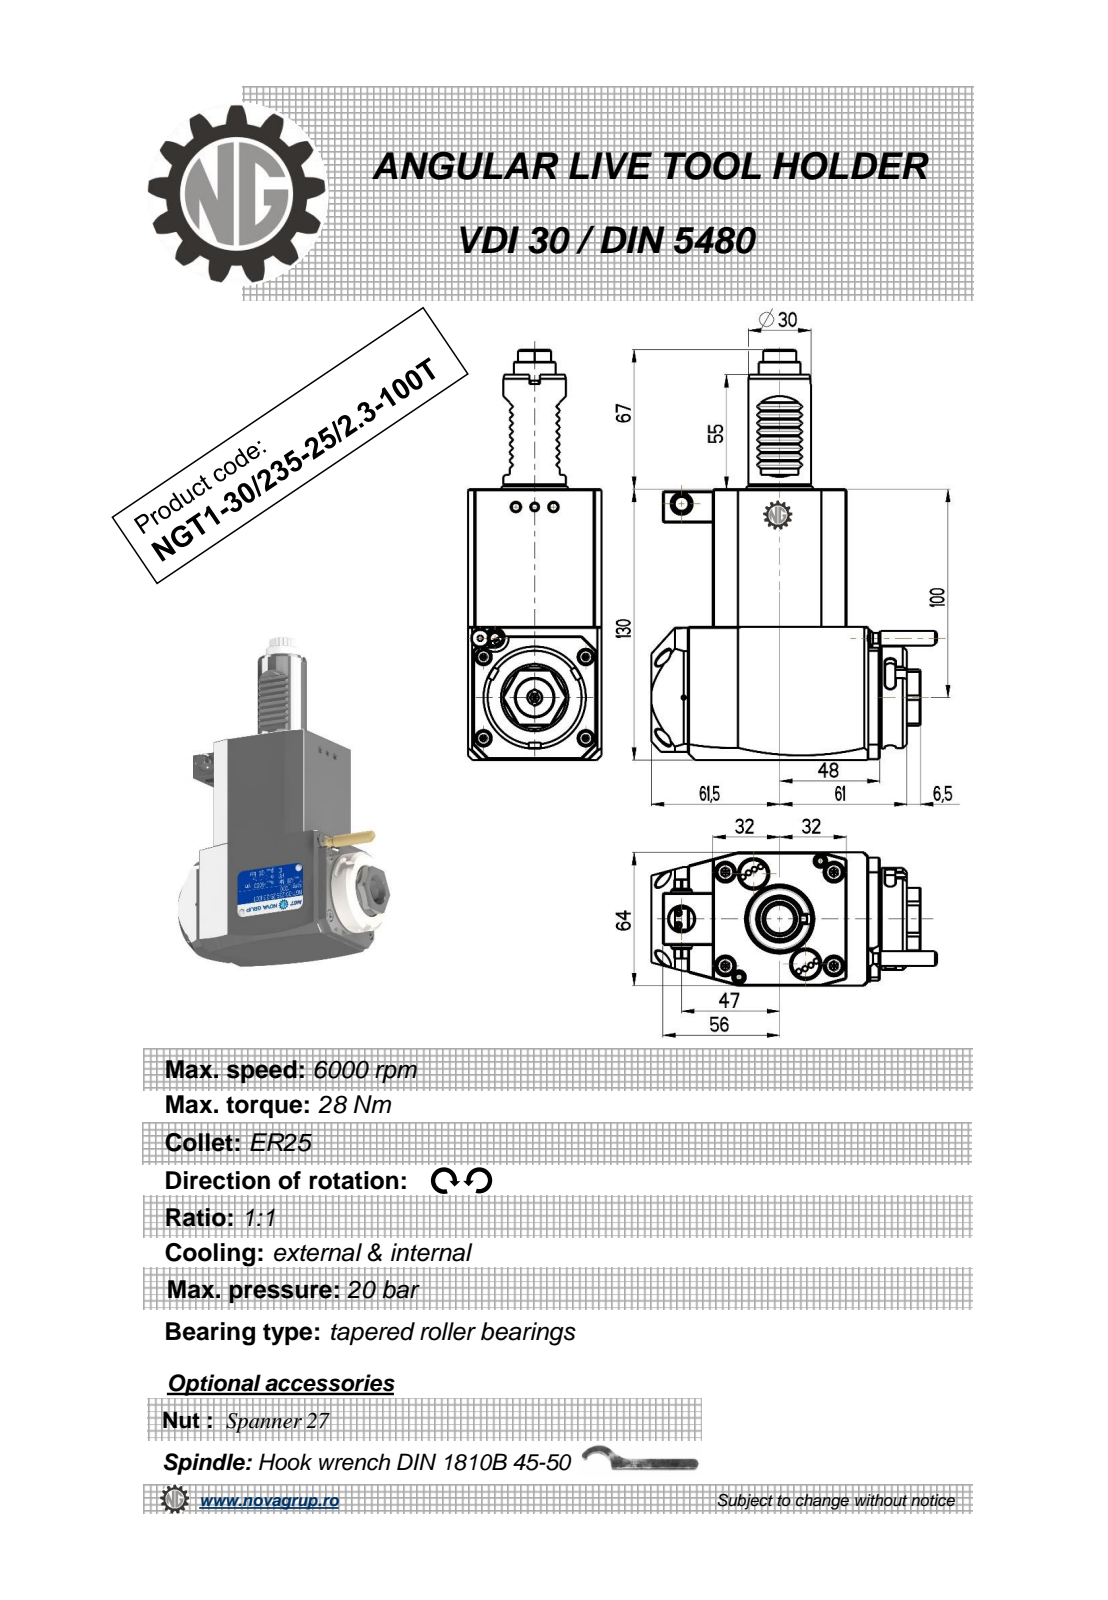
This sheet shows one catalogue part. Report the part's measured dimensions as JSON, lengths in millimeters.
{"part_name": "NGT1_30_235_25_1_3_100T", "step_written_by": "PRO/ENGINEER BY PARAMETRIC TECHNOLOGY CORPORATION, 2010280 (CONFIG_CONTROL_DESIGN)", "units": "millimeters", "bodies": {"solids": 1, "faces": 466, "planar": 215, "cylindrical": 161, "other": 90}, "overall_size": [197, 136.88, 64], "volume_mm3": 737988, "surface_area_mm2": 62270, "round_holes": [[2.5, 1], [3, 1], [9.5, 1], [12, 1], [18, 1]], "round_bosses_or_shafts": [[8, 2], [49, 1], [42, 1], [30, 1], [20, 1], [10, 1], [7, 1], [5, 1]], "partial_cylinders_radius": [[1.98, 36], [0.3, 16], [2.5, 6], [180, 2], [3.85, 1], [4.25, 1], [4.5, 1], [7.08, 1]], "face_to_face_distances": [64, 130, 16, 80, 72.18, 13, 93.5, 29.5, 109.5, 66], "hole_center_spacings": [34.25, 65.8, 91.5]}
